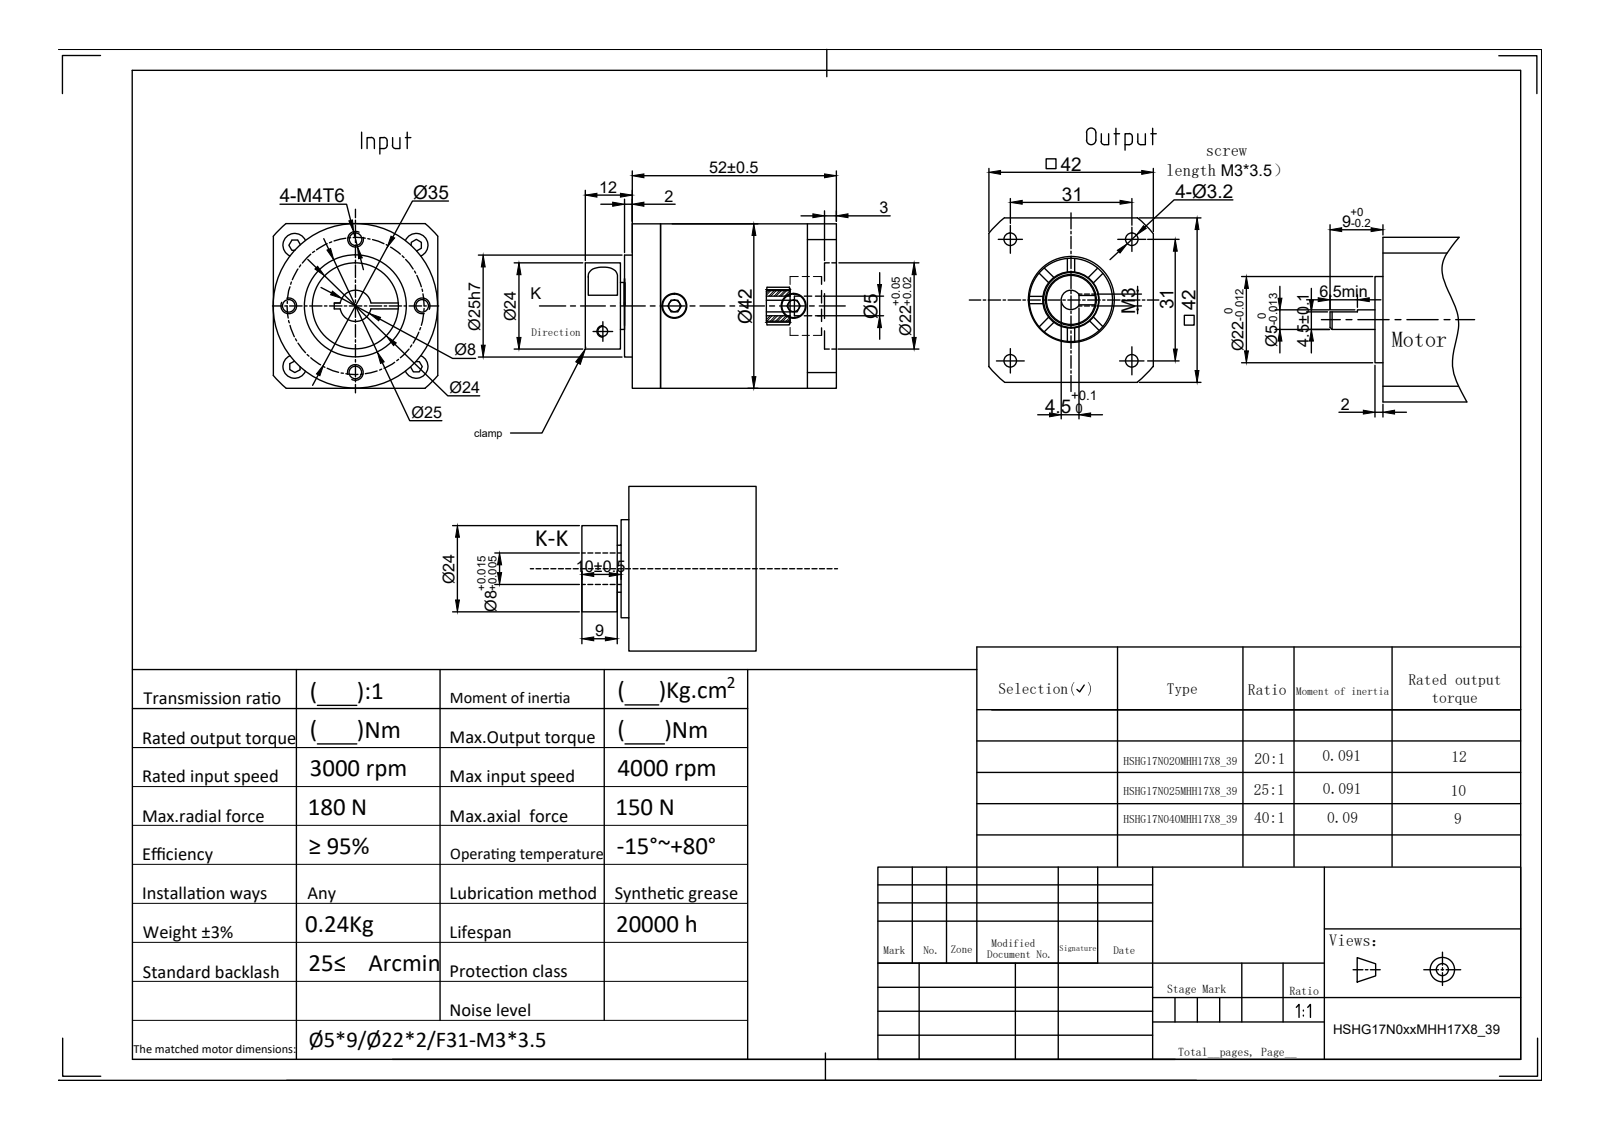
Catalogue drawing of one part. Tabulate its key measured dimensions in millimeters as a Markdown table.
| quantity | value |
| --- | --- |
| part name | HSHG17N0xxMHH17X8_39 |
| STEP written by | SolidWorks 2018 (AUTOMOTIVE_DESIGN) |
| units | millimeters |
| bodies | 7 solids, 310 faces (132 planar, 85 cylindrical, 93 other) |
| overall size | 67.5 × 42 × 42 |
| volume | 77 790 mm³ |
| surface area | 16 050 mm² |
| round holes (diameter × count) | 3.2 × 5, 3.3 × 4, 6.5 × 4, 2.5 × 2, 5 × 2, 4 × 1, 8 × 1, 15 × 1, 22 × 1 |
| round bosses / shafts (diameter × count) | 3 × 6, 5.5 × 5, 42 × 1, 25 × 1, 24 × 1, 14 × 1, 13 × 1 |
| partial cylindrical surfaces (radius × count) | 3 × 1, 27.5 × 1 |
| main face-to-face distances | 52, 42, 3, 10, 54, 49, 12, 64, 3.5, 2 |
| hole center spacings | 15.63, 36.46, 17.5, 21.92, 24.75, 31, 35, 43.84 |
